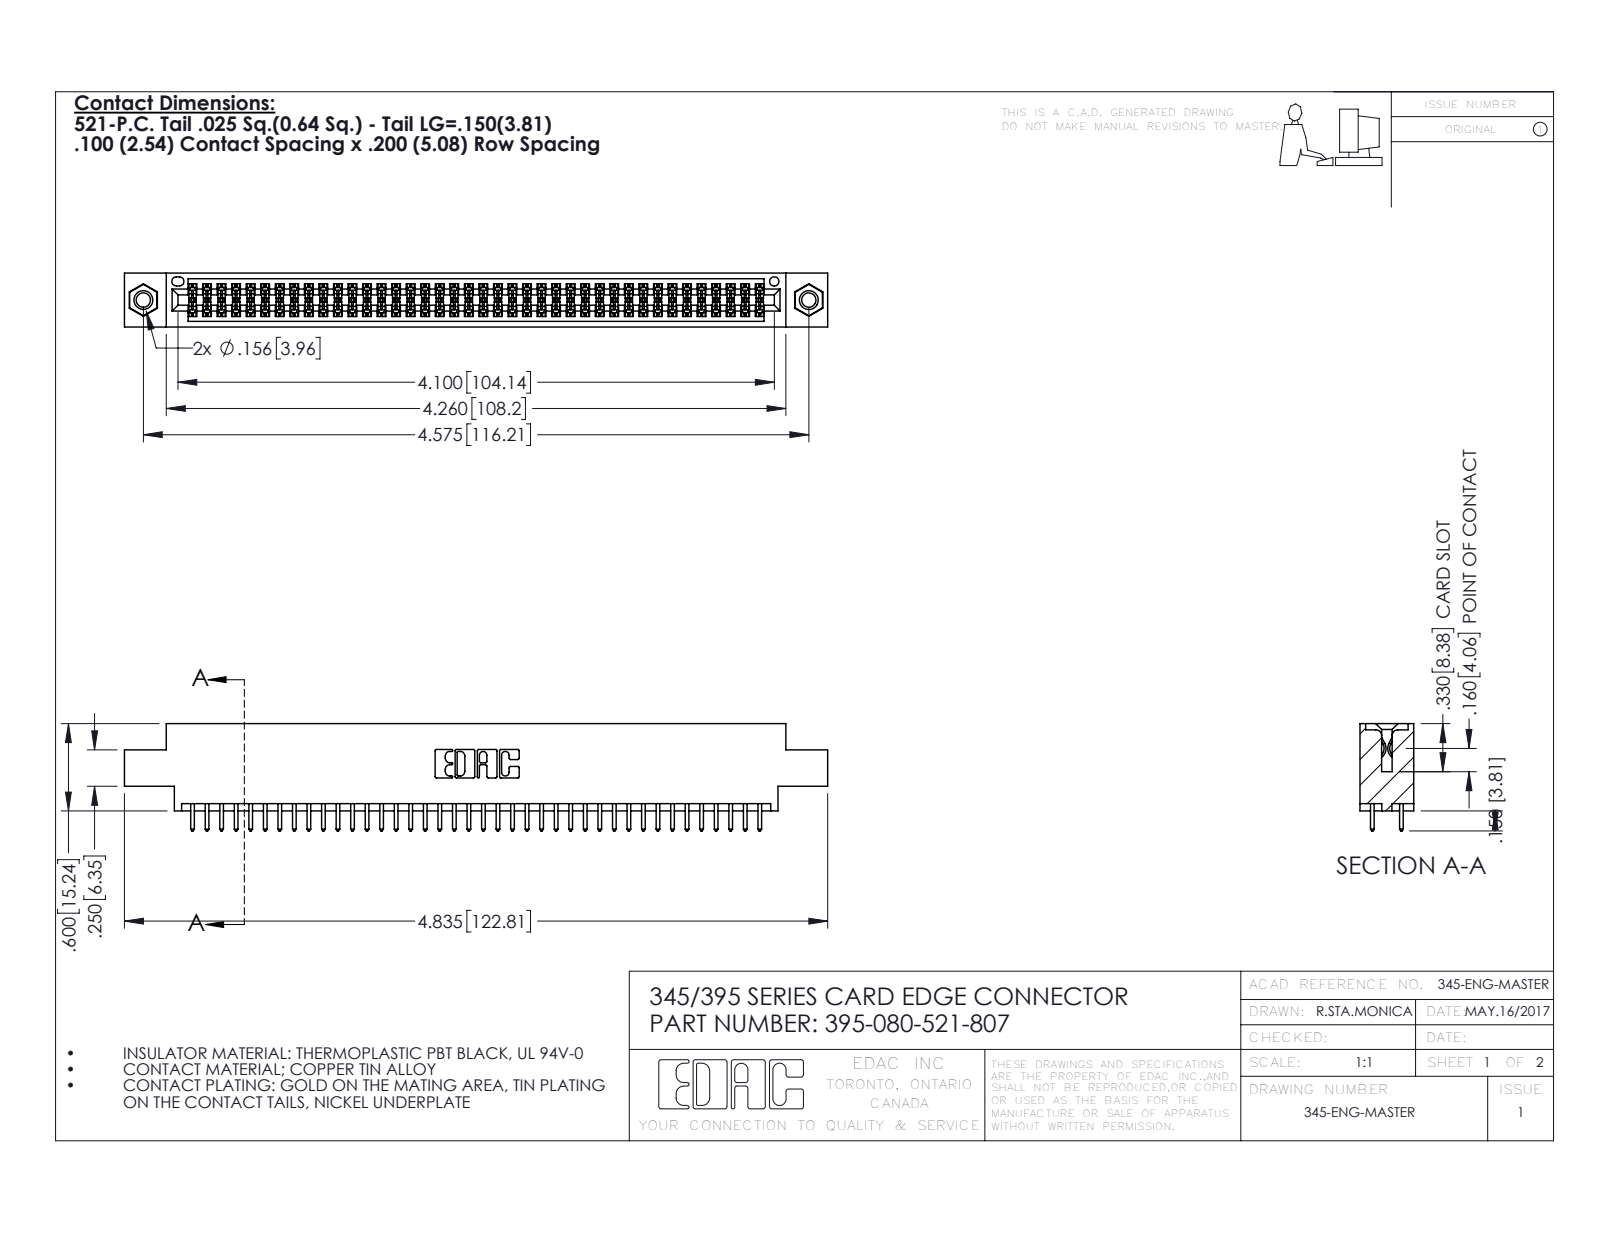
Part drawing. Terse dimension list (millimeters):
name: 345-250-001_345-250-005-103; 395-080-521-807; 345 Part_0.170 Offset - 0.156 Dia-TI; 345-292-001_345-293-121
written by: SolidWorks 2016 (CONFIG_CONTROL_DESIGN)
unit: mm
bodies: 83 solids, 4190 faces (2756 planar, 1418 cylindrical, 16 other)
size: 122.8 × 18.7 × 9.4
volume: 11 700 mm³; area: 17 290 mm²
holes: 2× ⌀2.5, 2× ⌀3.2, 2× ⌀4, 1× ⌀1.6
bosses: 2× ⌀3.9
rounds: 120× R0.2, 80× R0.3, 22× R0.3, 6× R0.2, 6× R0.8, 3× R0.7, 2× R0.4, 2× R0.5
face distances: 1.8, 7.6, 5.1, 9.4, 2.5, 6.9, 0.6, 5.7, 4.4, 3.8
hole spacings: 6.9, 110.2, 116.2
